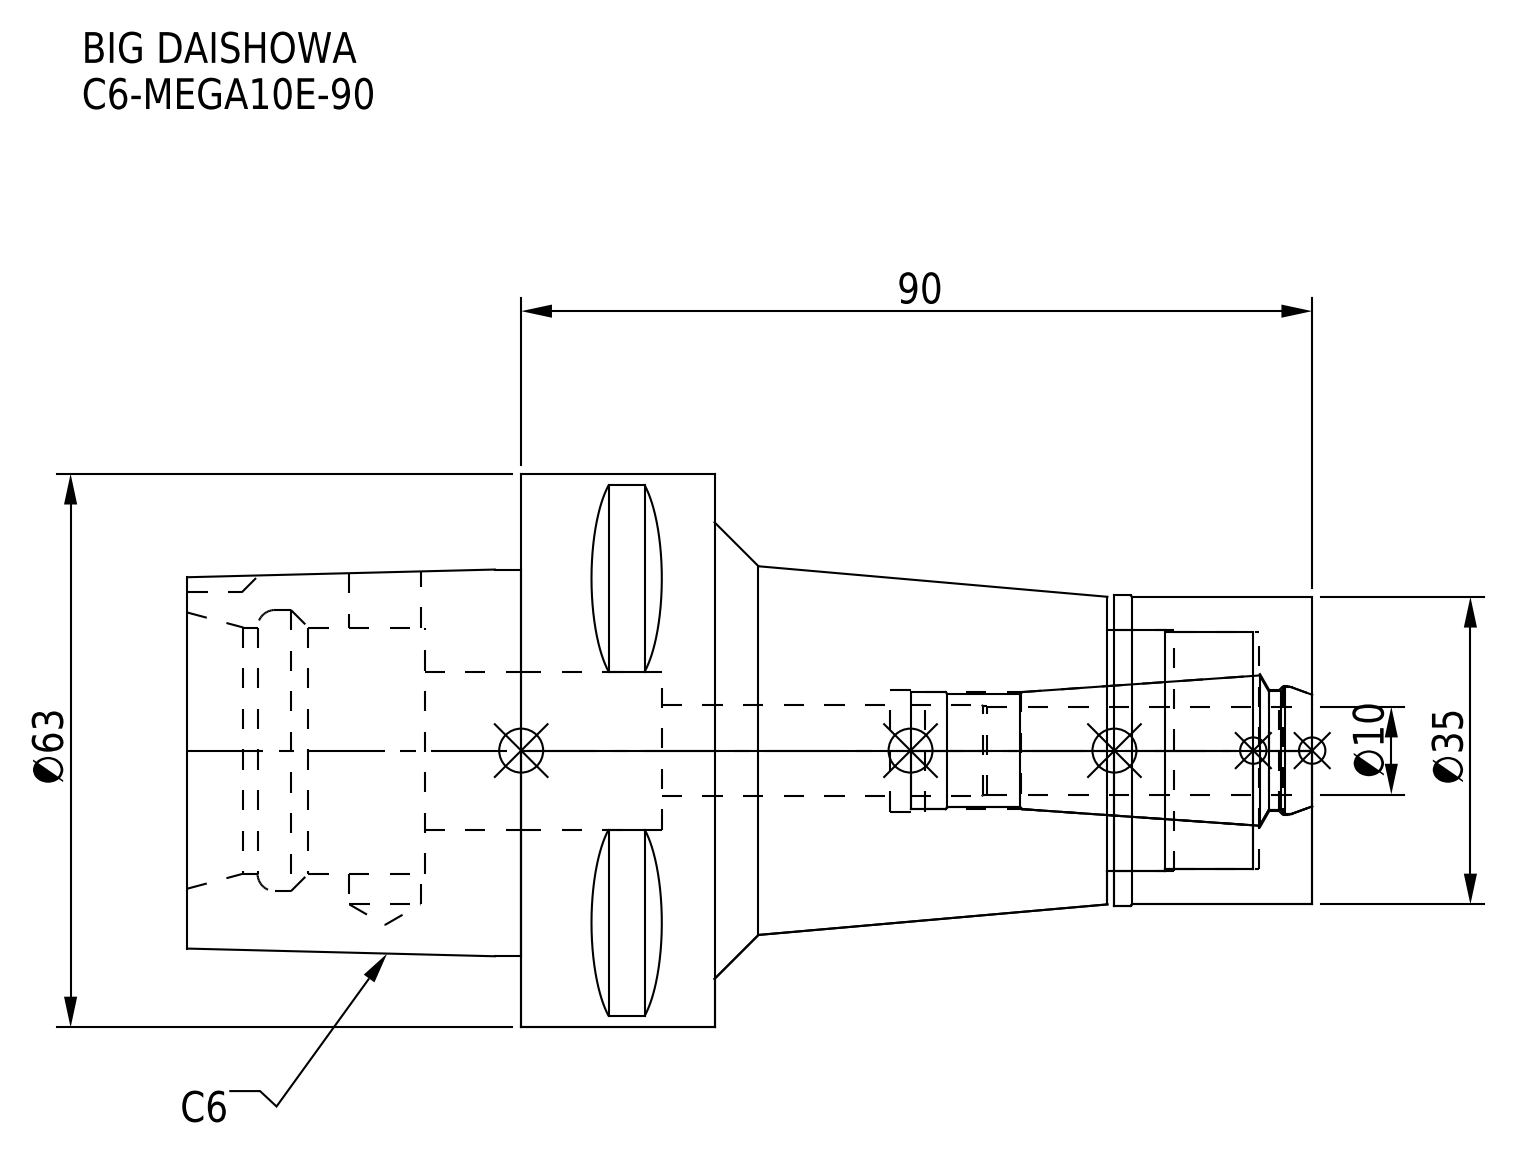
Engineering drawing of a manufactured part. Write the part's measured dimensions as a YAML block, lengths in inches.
part_name: "C6-MEGA10E-90-100.stp; MEN10_1.stp; C6-MEGA10E-90_1.stp; DXF_TEMP_ASSY_ASM_4_ASM.stp (+3 more)"
step_written_by: "SolidWorks 2019 (CONFIG_CONTROL_DESIGN)"
units: inches
bodies: {solids: 2, faces: 97, planar: 36, cylindrical: 37, other: 24}
overall_size: [5.039, 2.48, 2.48]
volume: 9.96
surface_area: 53.59
round_holes:
  - {diameter: 0.319, count: 1}
  - {diameter: 0.409, count: 1}
  - {diameter: 0.524, count: 1}
  - {diameter: 0.543, count: 1}
  - {diameter: 0.547, count: 1}
  - {diameter: 0.579, count: 1}
  - {diameter: 0.709, count: 1}
  - {diameter: 1.063, count: 1}
  - {diameter: 1.083, count: 1}
  - {diameter: 1.102, count: 1}
  - {diameter: 1.26, count: 1}
round_bosses_or_shafts:
  - {diameter: 2.48, count: 1}
  - {diameter: 1.39, count: 1}
  - {diameter: 1.378, count: 1}
partial_cylinders:
  - {radius: 0.197, count: 1}
face_to_face_distances: [2.677, 0.866, 3.543, 1.063, 1.496, 0.236, 5.039, 2.362, 0.886, 1.791]
